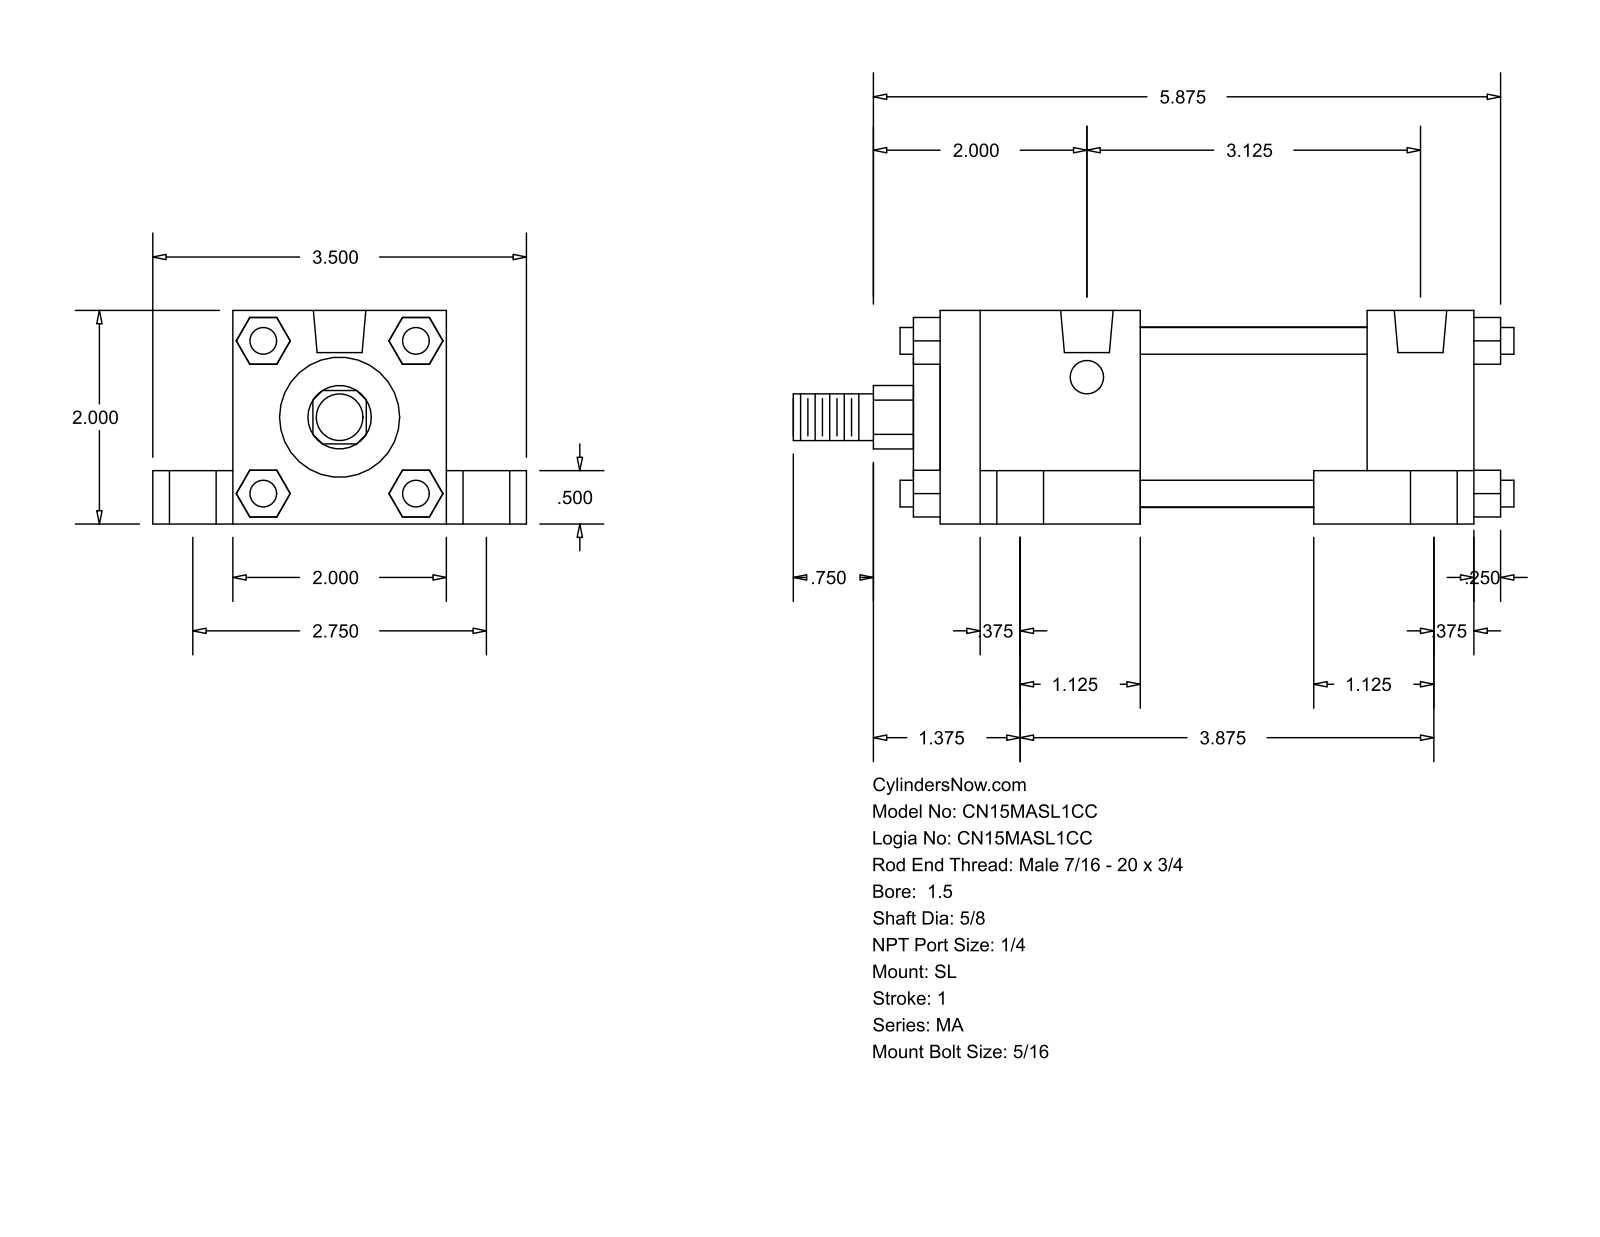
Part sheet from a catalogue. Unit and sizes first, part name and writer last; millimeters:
Units: millimetres
Overall size (bounding box): 171.45 × 88.9 × 50.8
Round holes (diameter × count): ⌀7.94 ×4, ⌀11.11 ×4, ⌀17.46 ×4, ⌀12.49 ×2
Round bosses / shafts (diameter × count): ⌀6.35 ×4, ⌀42.93 ×1, ⌀28.57 ×1, ⌀15.88 ×1, ⌀11.11 ×1
Partial cylindrical surfaces — rounded edges, fillets, slot ends (radius × count): R7.54 ×1
Main face-to-face distances: 50.8, 53.97, 19.05, 38.1, 127, 69.85, 12.7, 9.52, 101.59, 25.41
Hole centre spacings: 35.06, 38.36, 69.84, 79.38, 89.63, 98.43, 101.46, 120.69
Bodies: 0 solids, 148 faces (112 planar, 36 cylindrical, 0 other)
Part name (STEP PRODUCT): MA_SL__0150_0.625
STEP written by: GSSL Pune (CONFIG_CONTROL_DESIGN)
